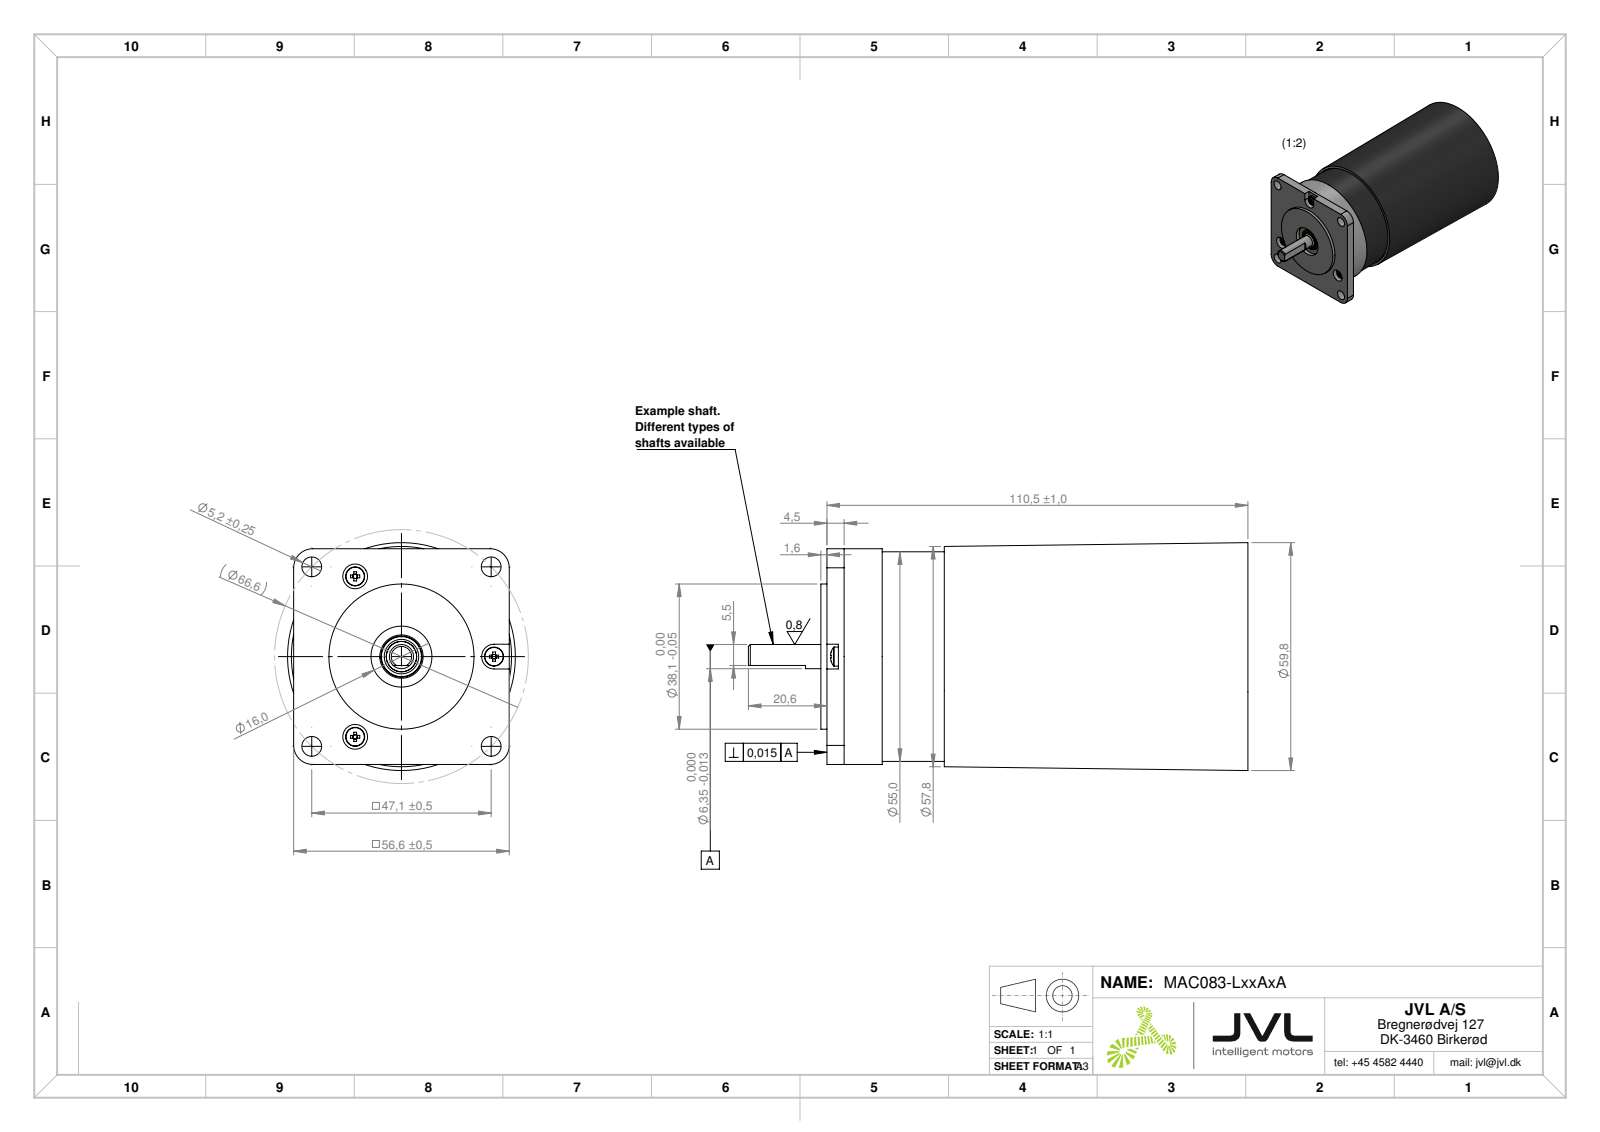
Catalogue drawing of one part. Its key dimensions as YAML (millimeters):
part_name: "Shaft variants MAC083-320 (base)_Ø6.35 L20.6 D-shaped; MAC083-320 (base)_MAC083; 5972K501_Ball Bearing_5972K501; MAC083-XXXXXX-X (+2 more)"
step_written_by: "SolidWorks 2023 (AUTOMOTIVE_DESIGN)"
units: millimeters
bodies: {solids: 19, faces: 576, planar: 229, cylindrical: 129, other: 218}
overall_size: [131.12, 59.8, 59.8]
volume: 121104
surface_area: 54189
round_holes:
  - {diameter: 2.05, count: 6}
  - {diameter: 5.2, count: 4}
  - {diameter: 2.5, count: 3}
  - {diameter: 6.5, count: 2}
  - {diameter: 8, count: 1}
  - {diameter: 9, count: 1}
  - {diameter: 10, count: 1}
  - {diameter: 10.76, count: 1}
  - {diameter: 11.37, count: 1}
  - {diameter: 16, count: 1}
  - {diameter: 17.18, count: 1}
  - {diameter: 18.09, count: 1}
round_bosses_or_shafts:
  - {diameter: 5, count: 3}
  - {diameter: 2.5, count: 3}
  - {diameter: 2.25, count: 2}
  - {diameter: 56.6, count: 1}
  - {diameter: 56, count: 1}
  - {diameter: 55, count: 1}
  - {diameter: 38.1, count: 1}
  - {diameter: 28, count: 1}
partial_cylinders:
  - {radius: 1, count: 4}
  - {radius: 5, count: 4}
  - {radius: 2.5, count: 2}
  - {radius: 4, count: 2}
  - {radius: 3.25, count: 1}
  - {radius: 26.68, count: 1}
face_to_face_distances: [20.8, 53.7, 32.9, 6, 14.8, 47.7, 55.3, 49.3, 34.5, 1.6]
hole_center_spacings: [33.3, 42.52, 47.1, 24.8, 42.96, 0.51, 10.74, 11.34]
